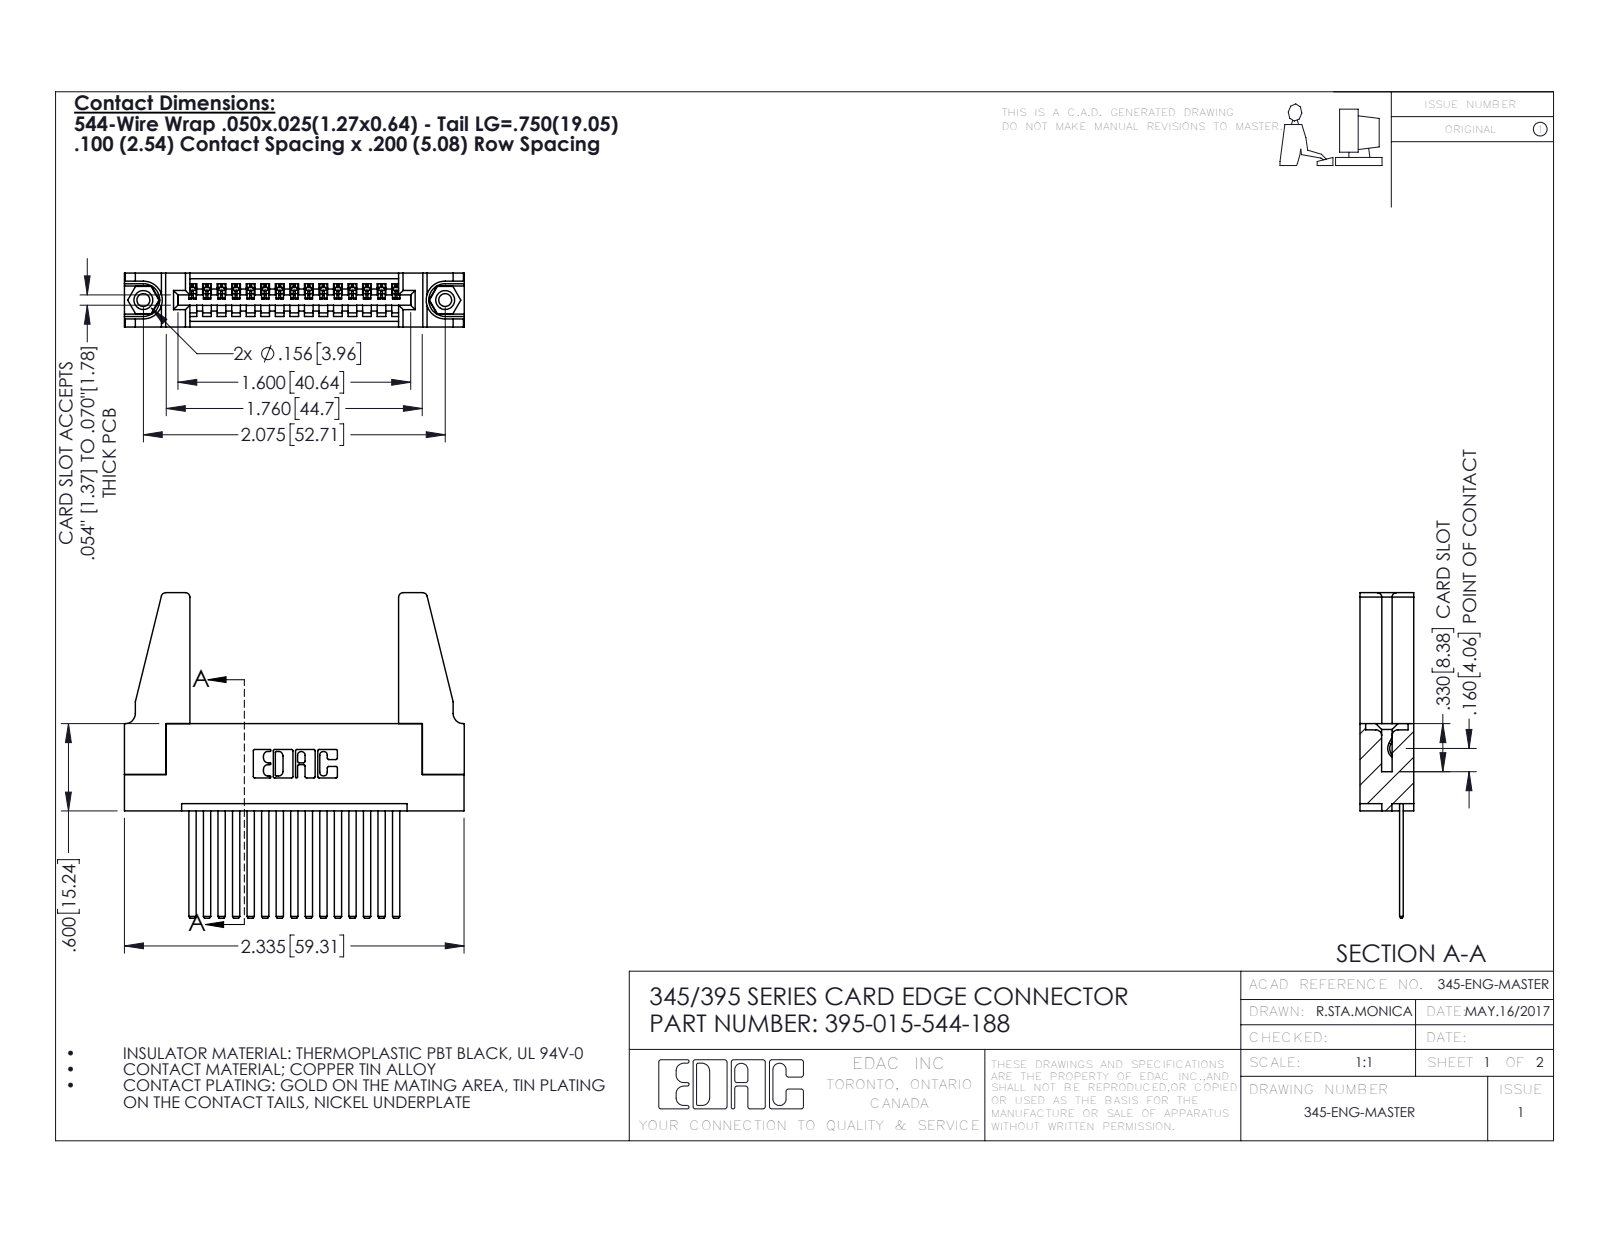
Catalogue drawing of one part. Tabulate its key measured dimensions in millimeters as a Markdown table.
| quantity | value |
| --- | --- |
| part name | 345-220-078_345-220-088; 345-292-001_345-293-144; 345 Part_Flush Mounting Lugs - 0.156 Dia-TH; 395-015-544-188 (+1 more) |
| STEP written by | SolidWorks 2016 (CONFIG_CONTROL_DESIGN) |
| units | millimeters |
| bodies | 20 solids, 1030 faces (692 planar, 322 cylindrical, 16 other) |
| overall size | 59.3 × 56.8 × 9.4 |
| volume | 8 830 mm³ |
| surface area | 10 710 mm² |
| round holes (diameter × count) | 2.3 × 2, 3.2 × 2, 4 × 2, 1.6 × 1 |
| round bosses / shafts (diameter × count) | 3.9 × 2 |
| partial cylindrical surfaces (radius × count) | 0.2 × 30, 0.3 × 22, 0.8 × 8, 0.2 × 6, 0.8 × 6, 0.7 × 3, 0.8 × 2, 1 × 2 |
| main face-to-face distances | 1.8, 7.6, 9.4, 5.1, 2.5, 6.9, 0.6, 5.7, 3.8, 3.8 |
| hole center spacings | 6.9, 46.8, 52.7 |
